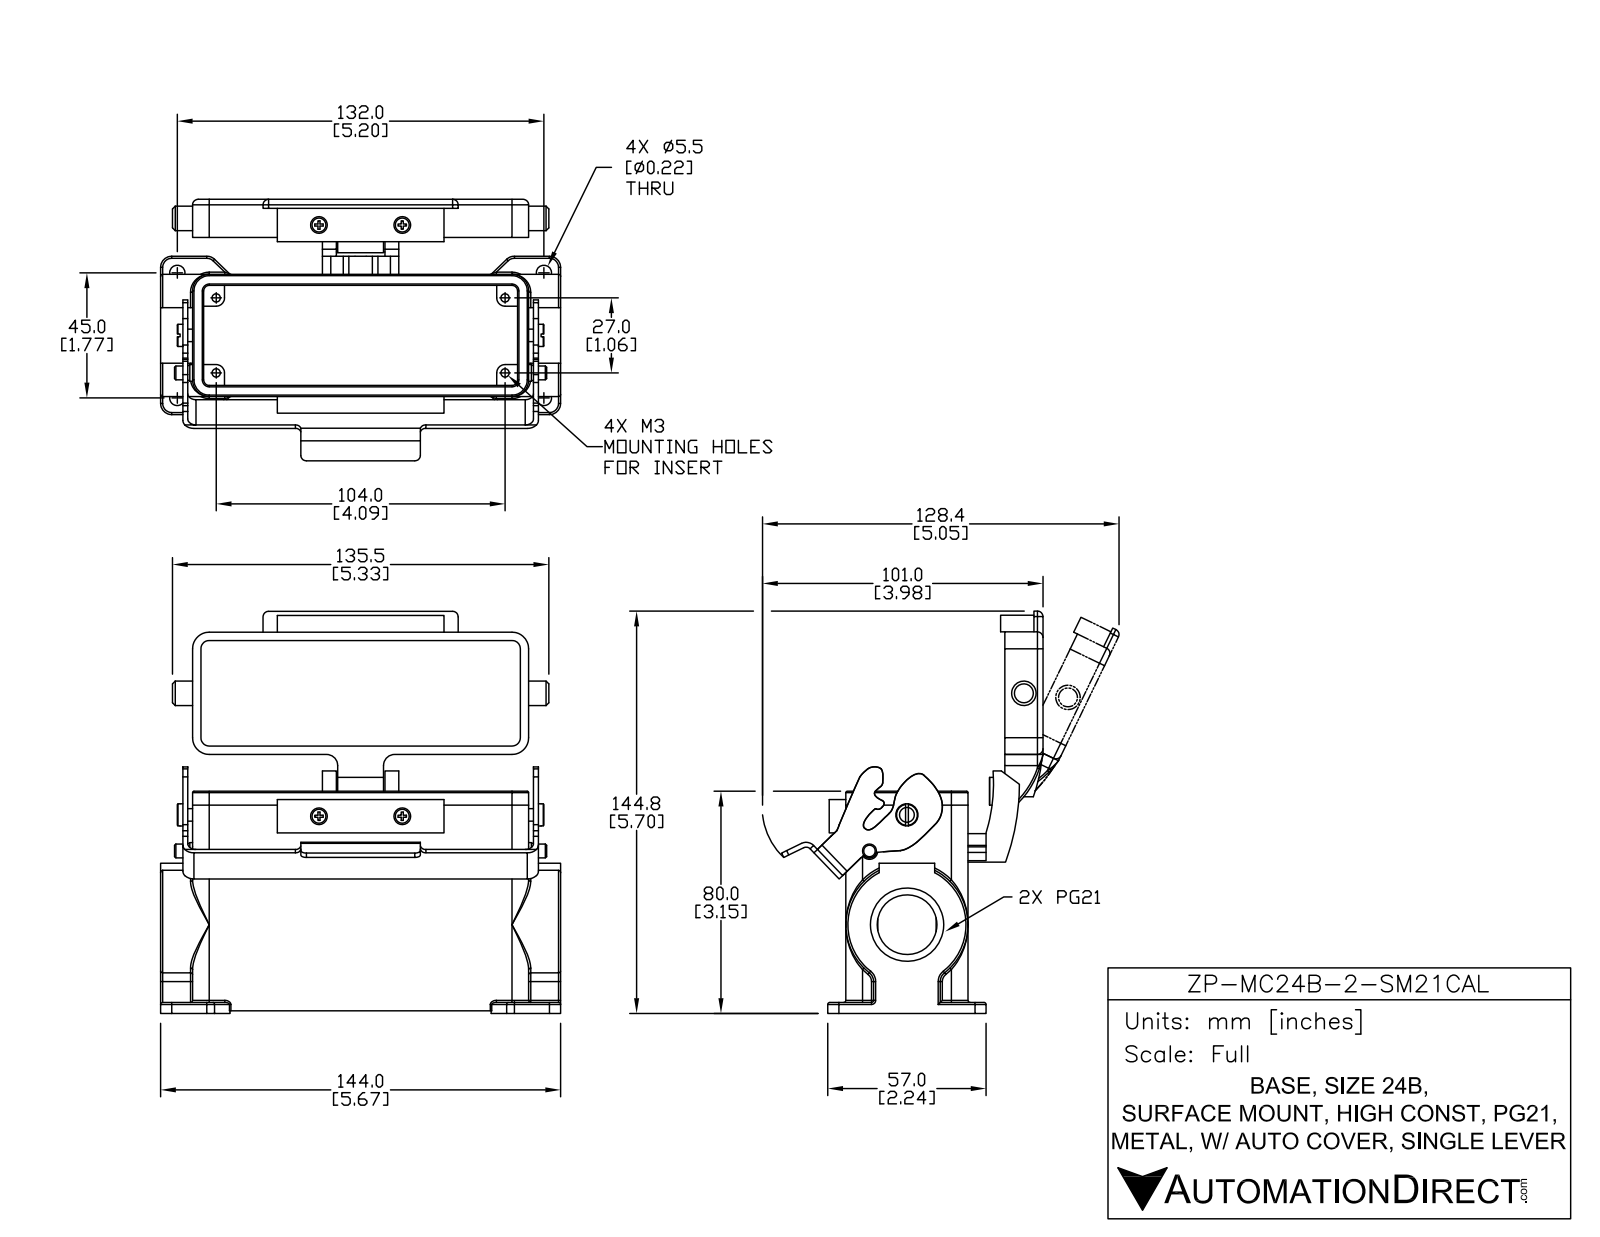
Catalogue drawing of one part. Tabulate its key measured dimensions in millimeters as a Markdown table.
| quantity | value |
| --- | --- |
| part name | ZP-MC24B-2-SM21CAL |
| STEP written by | SolidWorks 2014 (AUTOMOTIVE_DESIGN) |
| units | millimeters |
| bodies | 11 solids, 580 faces (242 planar, 190 cylindrical, 148 other) |
| overall size | 144.75 × 144 × 94.11 |
| volume | 203 207 mm³ |
| surface area | 108 561 mm² |
| round holes (diameter × count) | 3 × 4, 5.5 × 4, 4.5 × 1, 5.32 × 1, 21.5 × 1, 26.4 × 1 |
| round bosses / shafts (diameter × count) | 5 × 5, 8 × 2, 8.8 × 1, 6 × 1 |
| partial cylindrical surfaces (radius × count) | 0.75 × 25, 2 × 23, 4 × 14, 3 × 12, 0.5 × 8, 6 × 8, 21.95 × 2, 3.75 × 1 |
| main face-to-face distances | 4, 40, 44, 1.75, 36, 26.98, 30.98, 66.98, 70.98, 11.5 |
| hole center spacings | 16.64, 38.63, 118.34, 123.37, 27, 45, 104, 107.45 |
